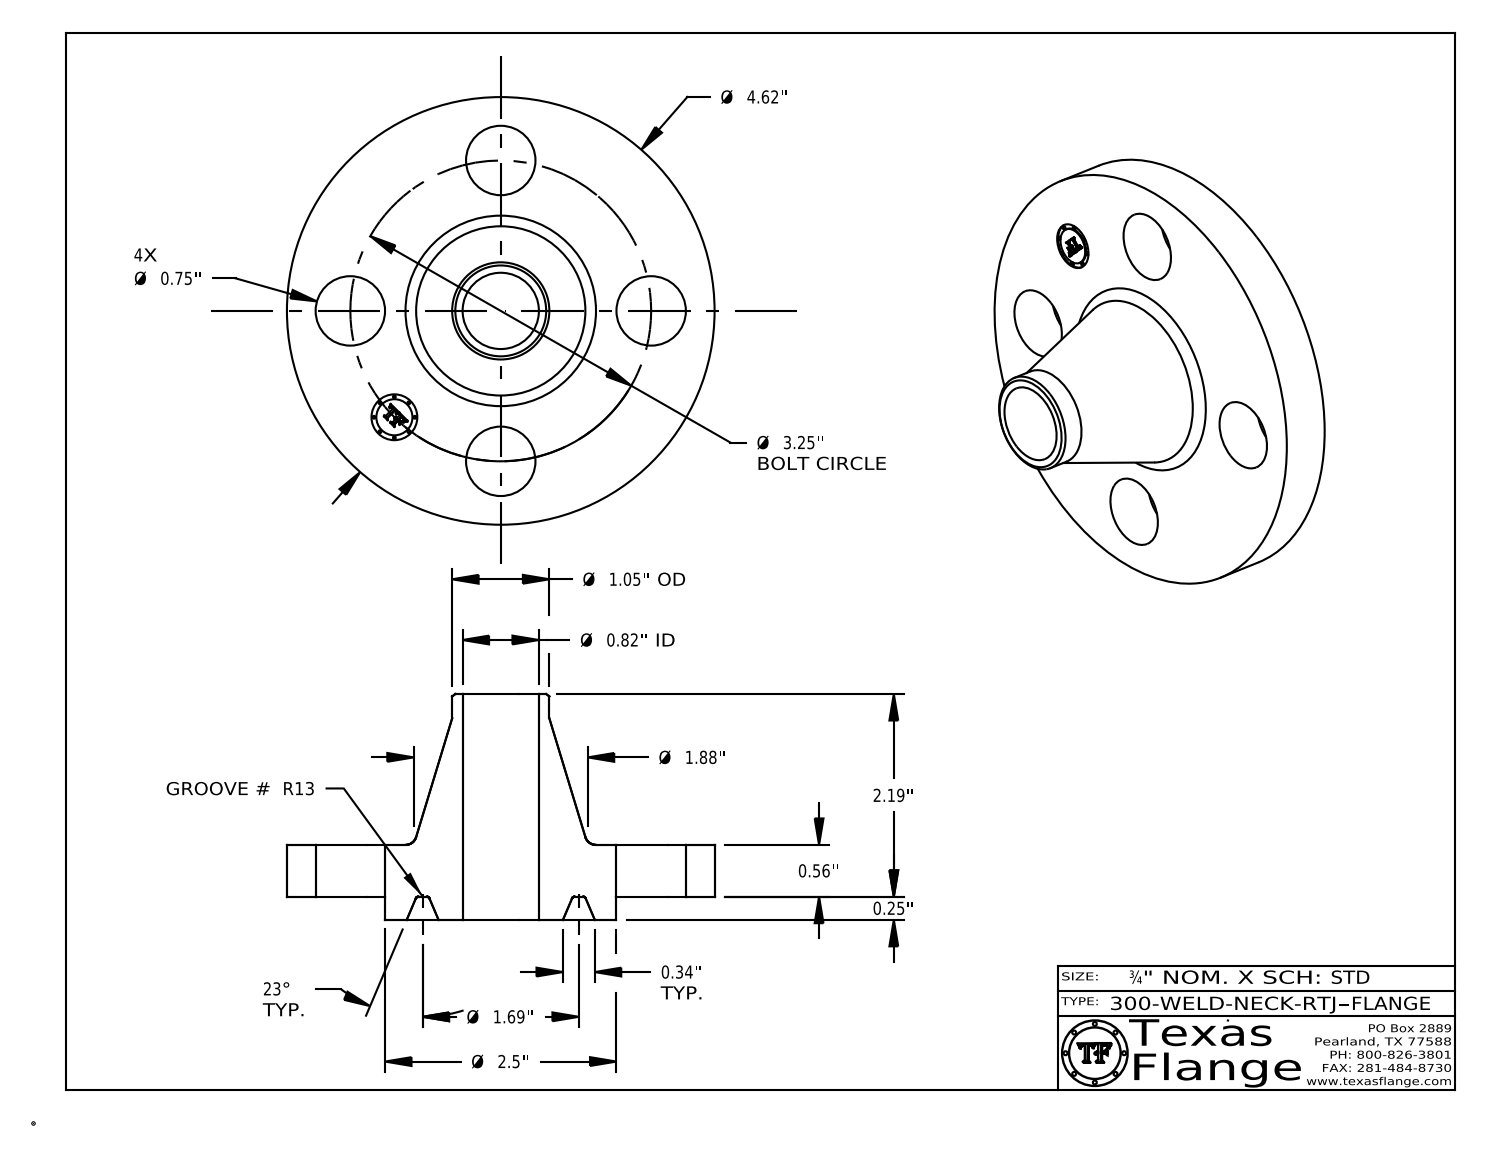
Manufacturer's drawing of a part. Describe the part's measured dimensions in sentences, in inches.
The part is named "300-WELD-NECK-RTJ". Its 3-D file was written by "CATIA V5 STEP AP214 (AUTOMOTIVE_DESIGN)". It is 1 solid with 421 faces: 371 planar, 36 cylindrical and 14 other. Overall it measures 4.62 by 4.62 by 2.44 inches. Its volume is 10.61 cubic inches and its surface area 57.74 square inches. Round holes: 4 of diameter 0.75, 1 of diameter 0.495, 1 of diameter 0.824. Round bosses or shafts: 8 of diameter 0.03, 1 of diameter 4.62, 1 of diameter 2.5, 1 of diameter 1.05, 1 of diameter 0.39. The main face-to-face distances are 0.56, 0.25, 0.81, 2.44, 2.19, 1.63, 0.795, 0.545, 0.015, 1.645. The hole center spacings are 1.625, 2.298, 1.244, 3.003, 3.25.
